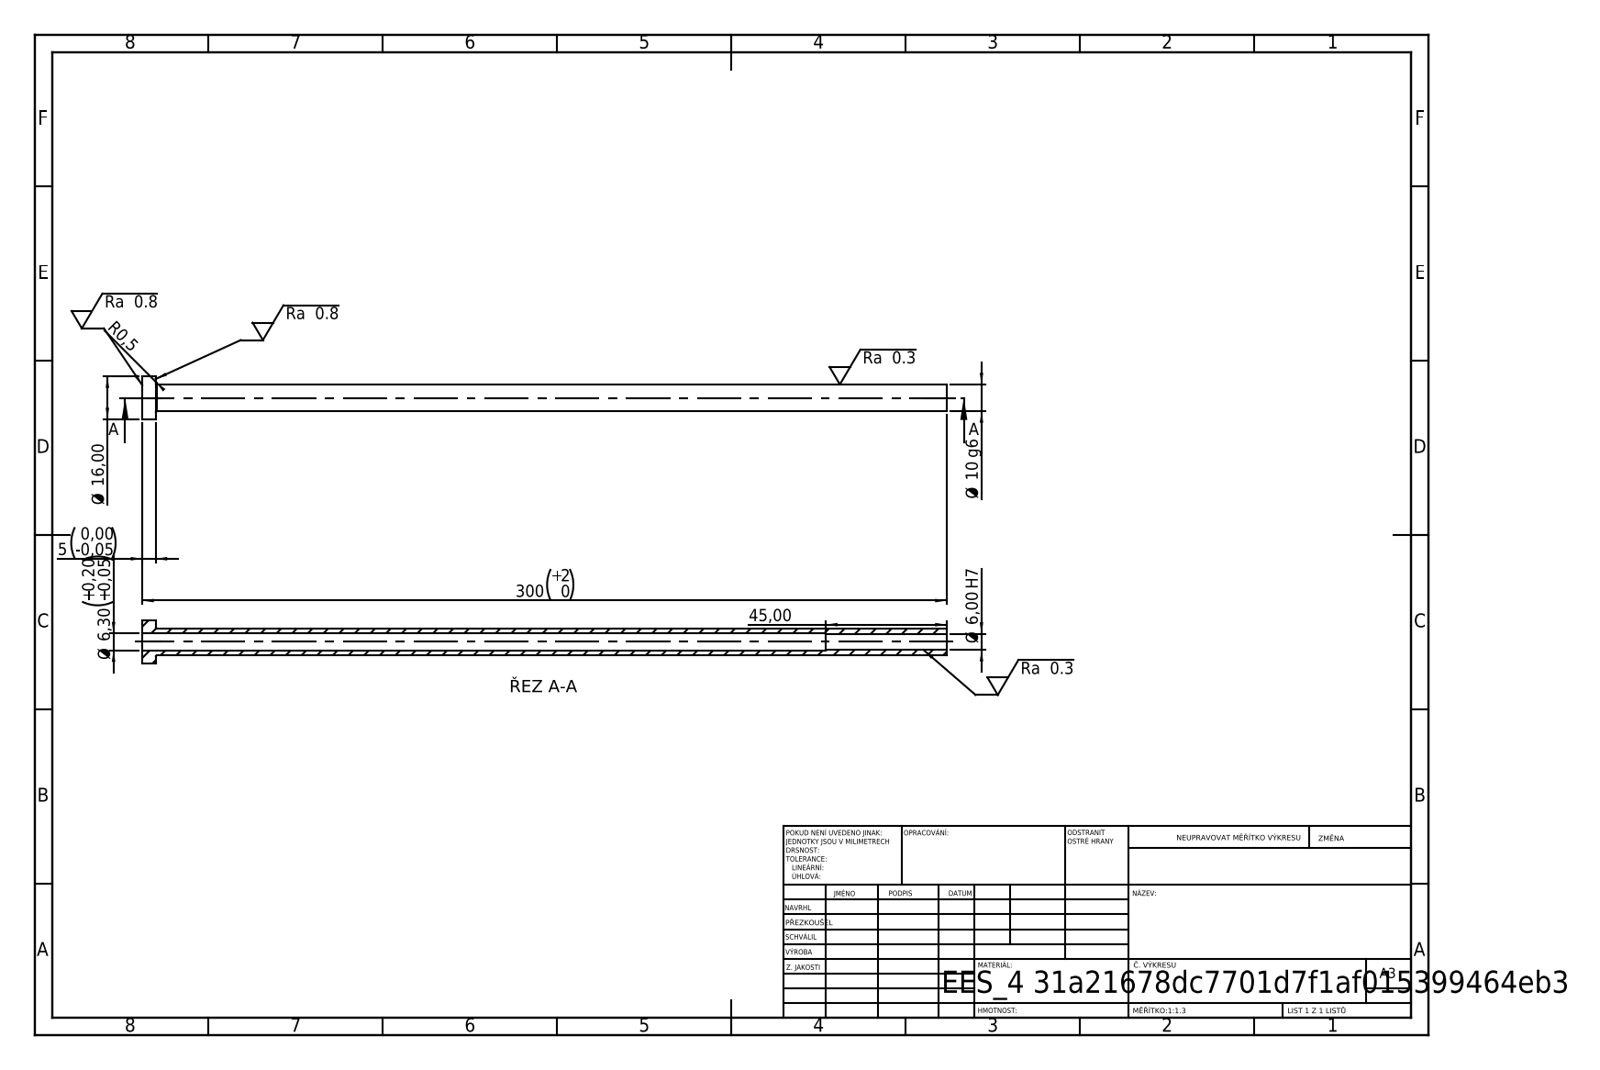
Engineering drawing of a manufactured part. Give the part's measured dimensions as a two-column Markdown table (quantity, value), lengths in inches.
| quantity | value |
| --- | --- |
| STEP written by | SolidWorks 2019 (CONFIG_CONTROL_DESIGN) |
| units | inches |
| bodies | 1 solid, 14 faces (4 planar, 8 cylindrical, 2 other) |
| overall size | 11.811 × 0.63 × 0.63 |
| volume | 0.913 in³ |
| surface area | 24.42 in² |
| round holes (diameter × count) | 0.236 × 1, 0.248 × 1 |
| round bosses / shafts (diameter × count) | 0.63 × 1, 0.394 × 1 |
| main face-to-face distances | 0.197, 11.811, 11.614, 10.039, 9.843, 1.772 |
